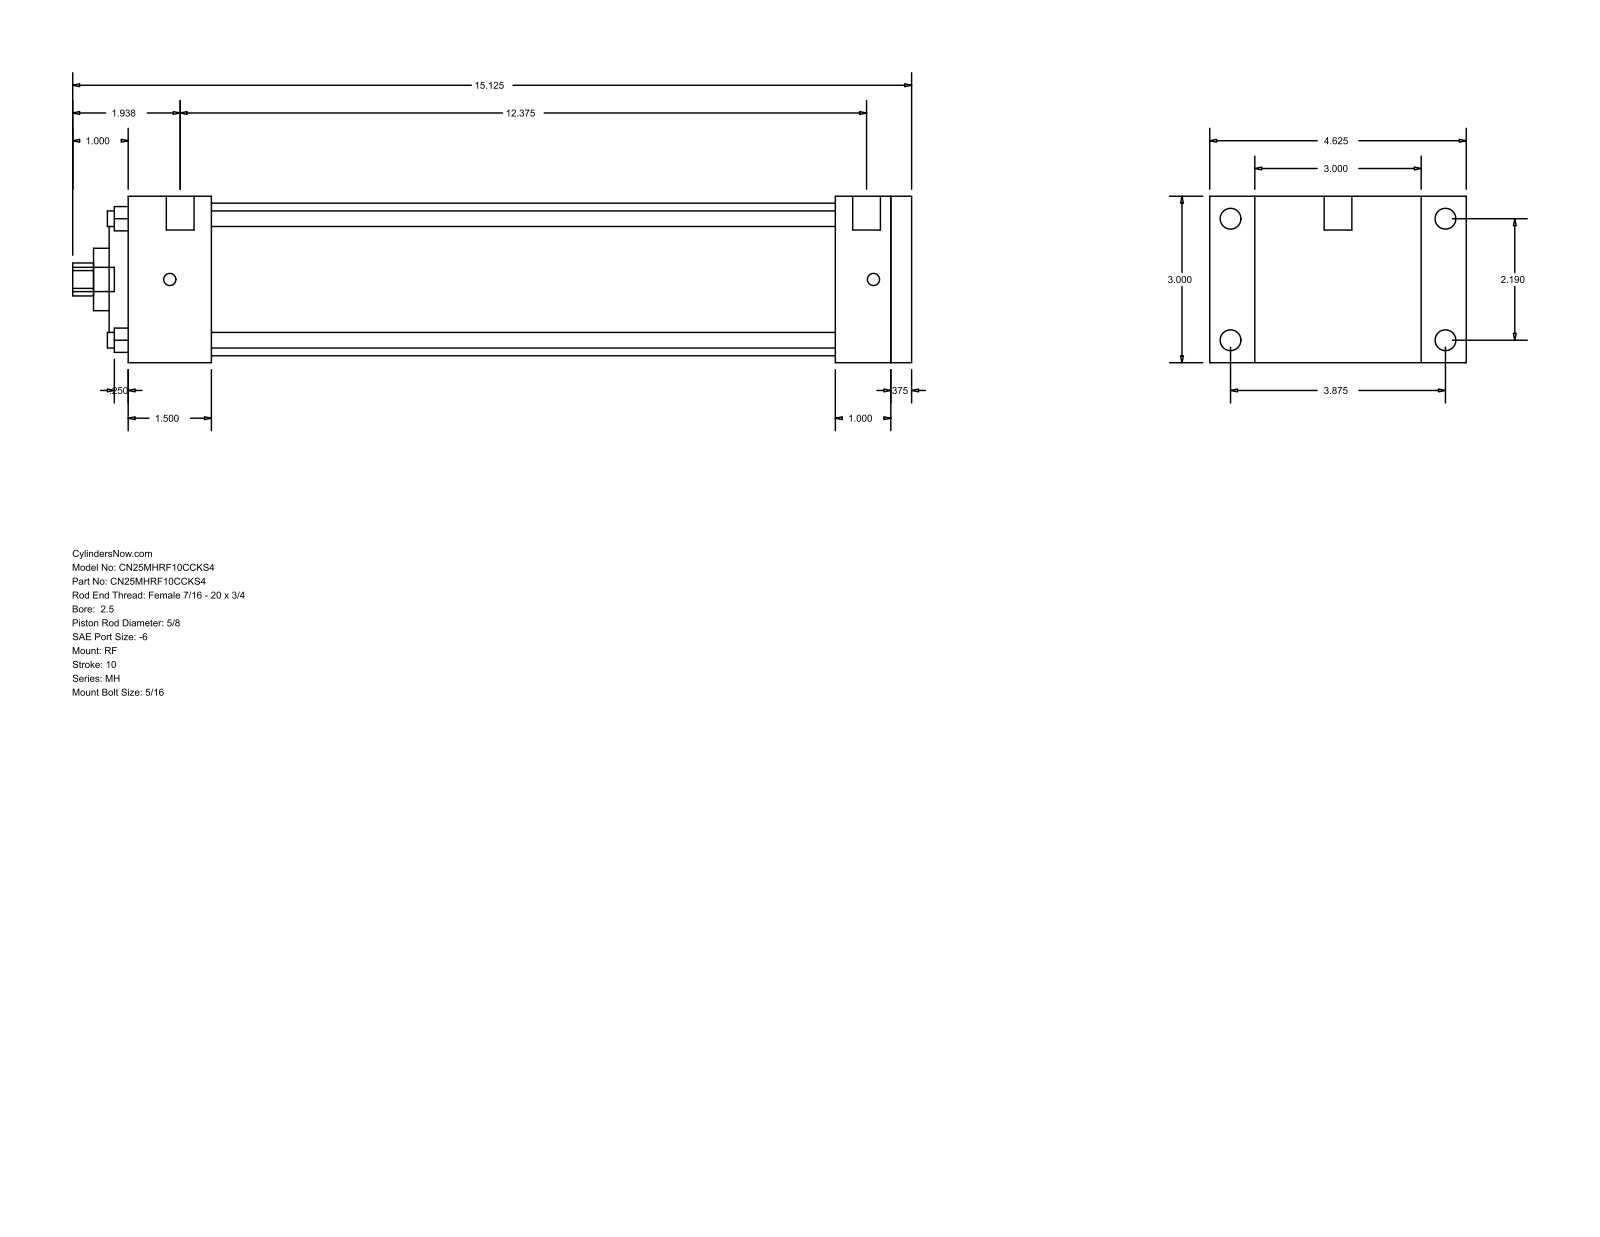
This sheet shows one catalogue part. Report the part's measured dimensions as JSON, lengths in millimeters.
{"part_name": "MH_RF__0250_0.625", "step_written_by": "GSSL Pune (CONFIG_CONTROL_DESIGN)", "units": "millimeters", "bodies": {"solids": 0, "faces": 94, "planar": 65, "cylindrical": 29, "other": 0}, "overall_size": [384.18, 117.47, 76.2], "round_holes": [[7.14, 4], [15.88, 1], [28.57, 1], [55.55, 1], [69.85, 1]], "round_bosses_or_shafts": [[9.53, 4], [5.56, 4], [12.7, 2], [11.11, 1]], "partial_cylinders_radius": [[7.54, 1]], "face_to_face_distances": [76.2, 9.53, 358.78, 349.25, 25.4, 323.85, 34.93, 38.1, 285.75, 311.15], "hole_center_spacings": [39.33, 55.62, 78.66]}
